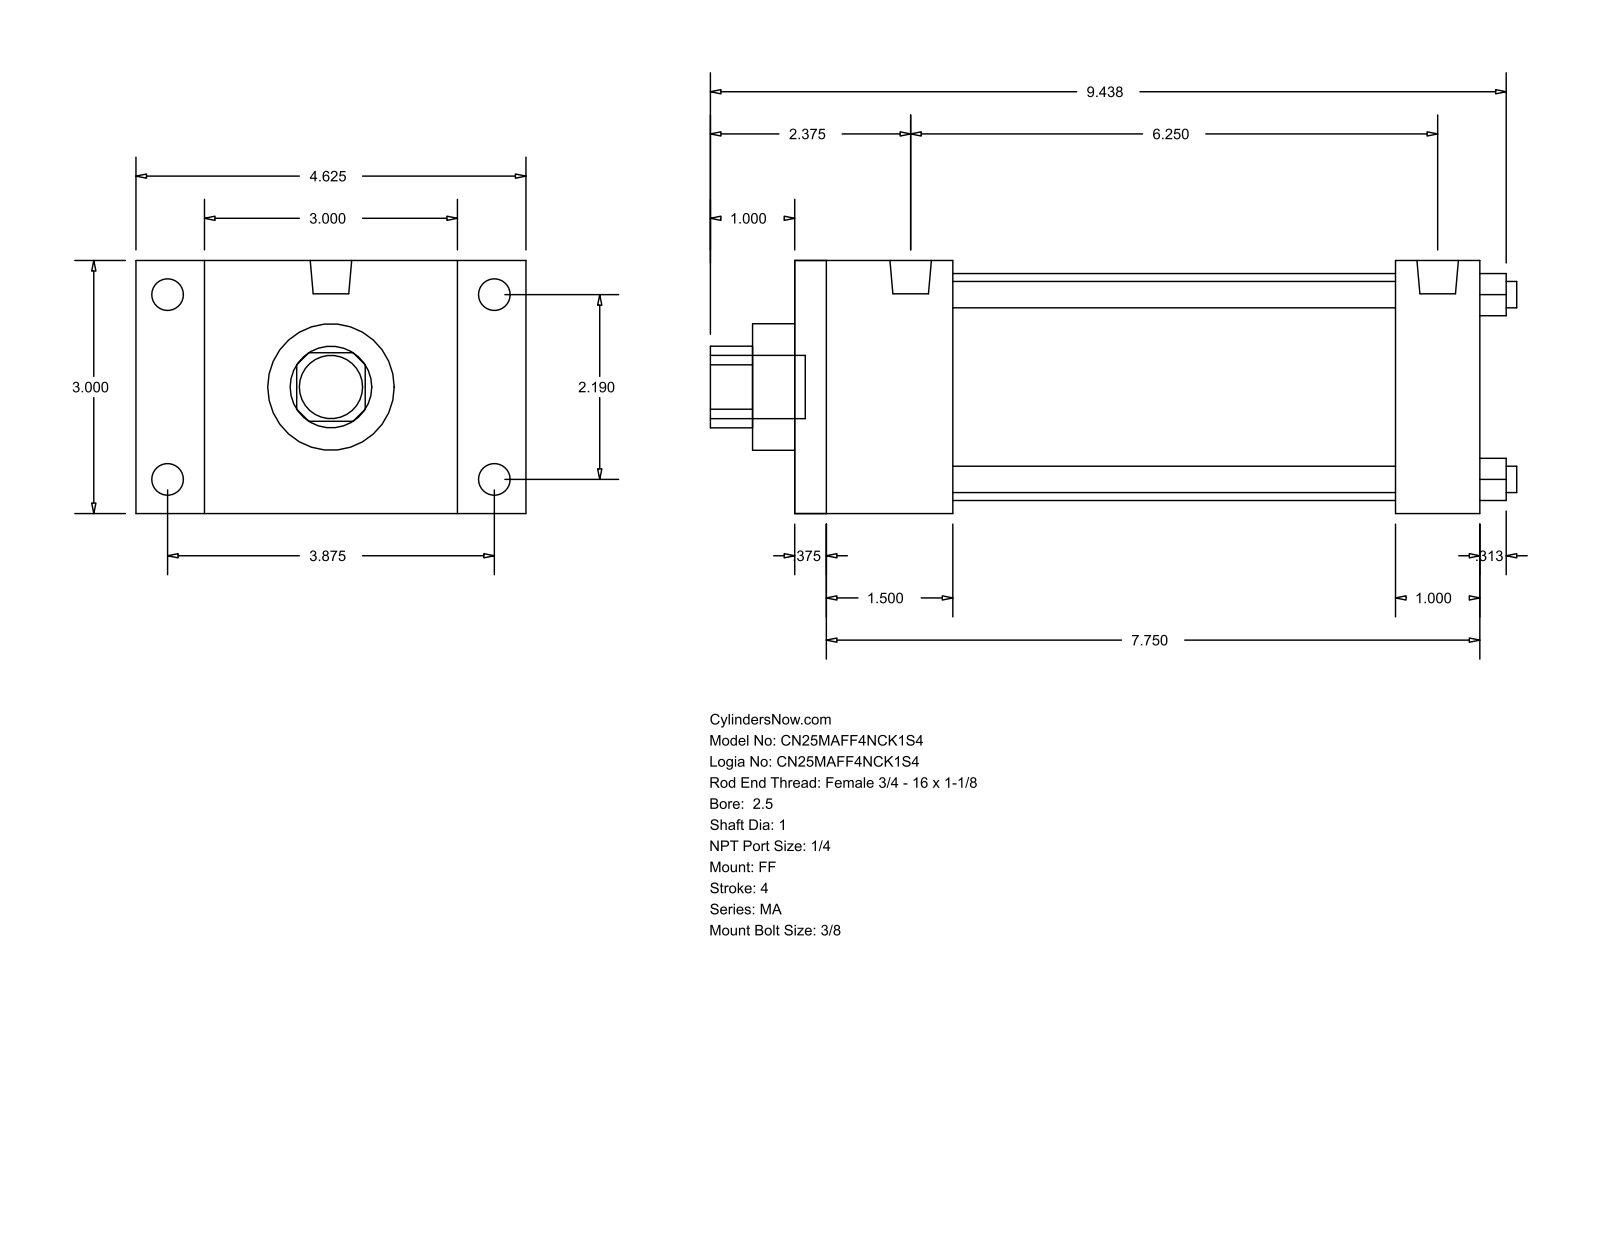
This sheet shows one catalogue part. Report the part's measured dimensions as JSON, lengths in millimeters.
{"part_name": "MA_FF__0250_1", "step_written_by": "GSSL Pune (CONFIG_CONTROL_DESIGN)", "units": "millimeters", "bodies": {"solids": 0, "faces": 92, "planar": 64, "cylindrical": 28, "other": 0}, "overall_size": [242.89, 117.47, 76.2], "round_holes": [[7.94, 4], [25.4, 1], [38.1, 1], [68.33, 1]], "round_bosses_or_shafts": [[9.53, 4], [7.94, 4], [12.49, 2], [19.05, 1]], "partial_cylinders_radius": [[12.29, 1]], "face_to_face_distances": [76.2, 206.38, 9.52, 196.86, 25.4, 47.63, 180.98, 38.11, 171.46, 133.35], "hole_center_spacings": [39.33, 55.62, 78.66]}
